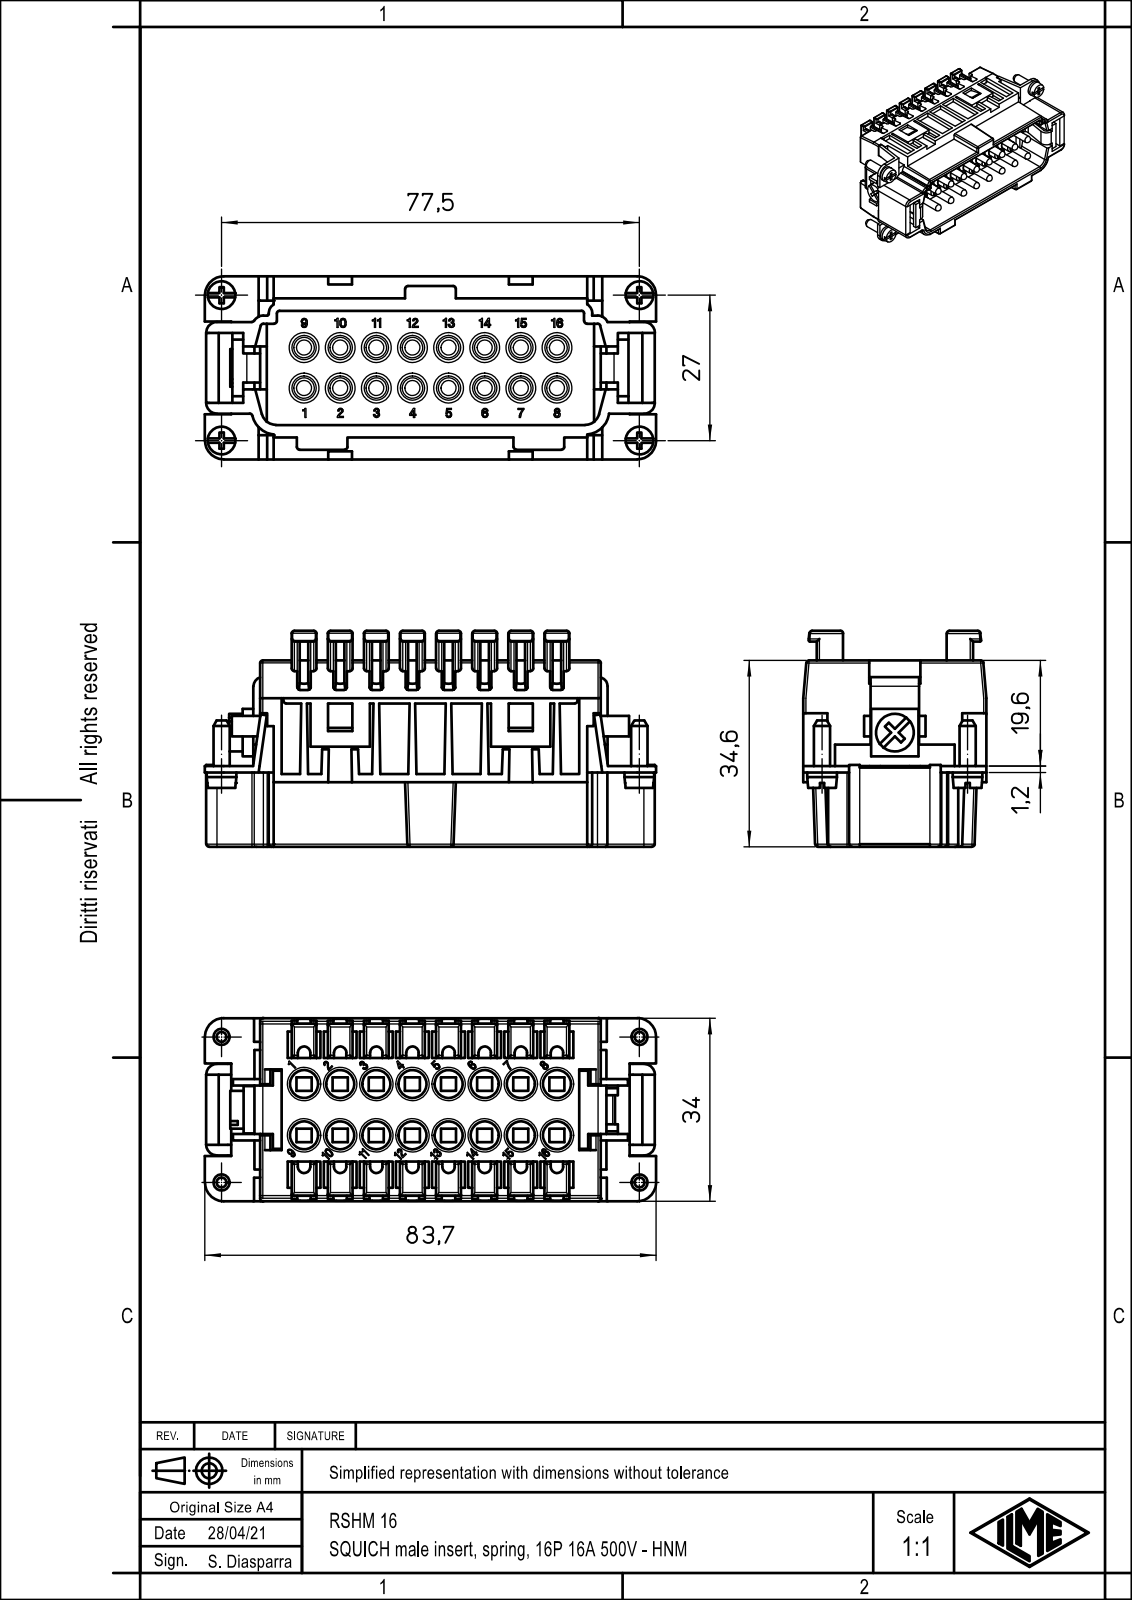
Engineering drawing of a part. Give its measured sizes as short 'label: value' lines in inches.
name: RSHM_16
written by: Creo Elements/Direct Modeling 20.1B 02-Apr-2019 (C) Parametric Technology GmbH (AUTOMOTIVE_DESIGN)
unit: in
bodies: 1 solid, 2127 faces (1267 planar, 525 cylindrical, 335 other)
size: 3.295 × 1.579 × 1.339
volume: 3.131 in³; area: 40.55 in²
holes: 16× ⌀0.205, 1× ⌀0.13
bosses: 16× ⌀0.098, 4× ⌀0.217, 4× ⌀0.118, 1× ⌀0.276
rounds: 154× R0.02, 35× R0.012, 34× R0.008, 16× R0.045, 10× R0.079, 4× R0.138, 2× R0.039, 2× R0.051
face distances: 0.059, 0.791, 0.193, 1.028, 1.087, 0.252, 0.098, 1.28, 0.988, 0.835
hole spacings: 0.264, 0.457, 0.528, 0.647, 0.791, 0.875, 0.374, 1.055
